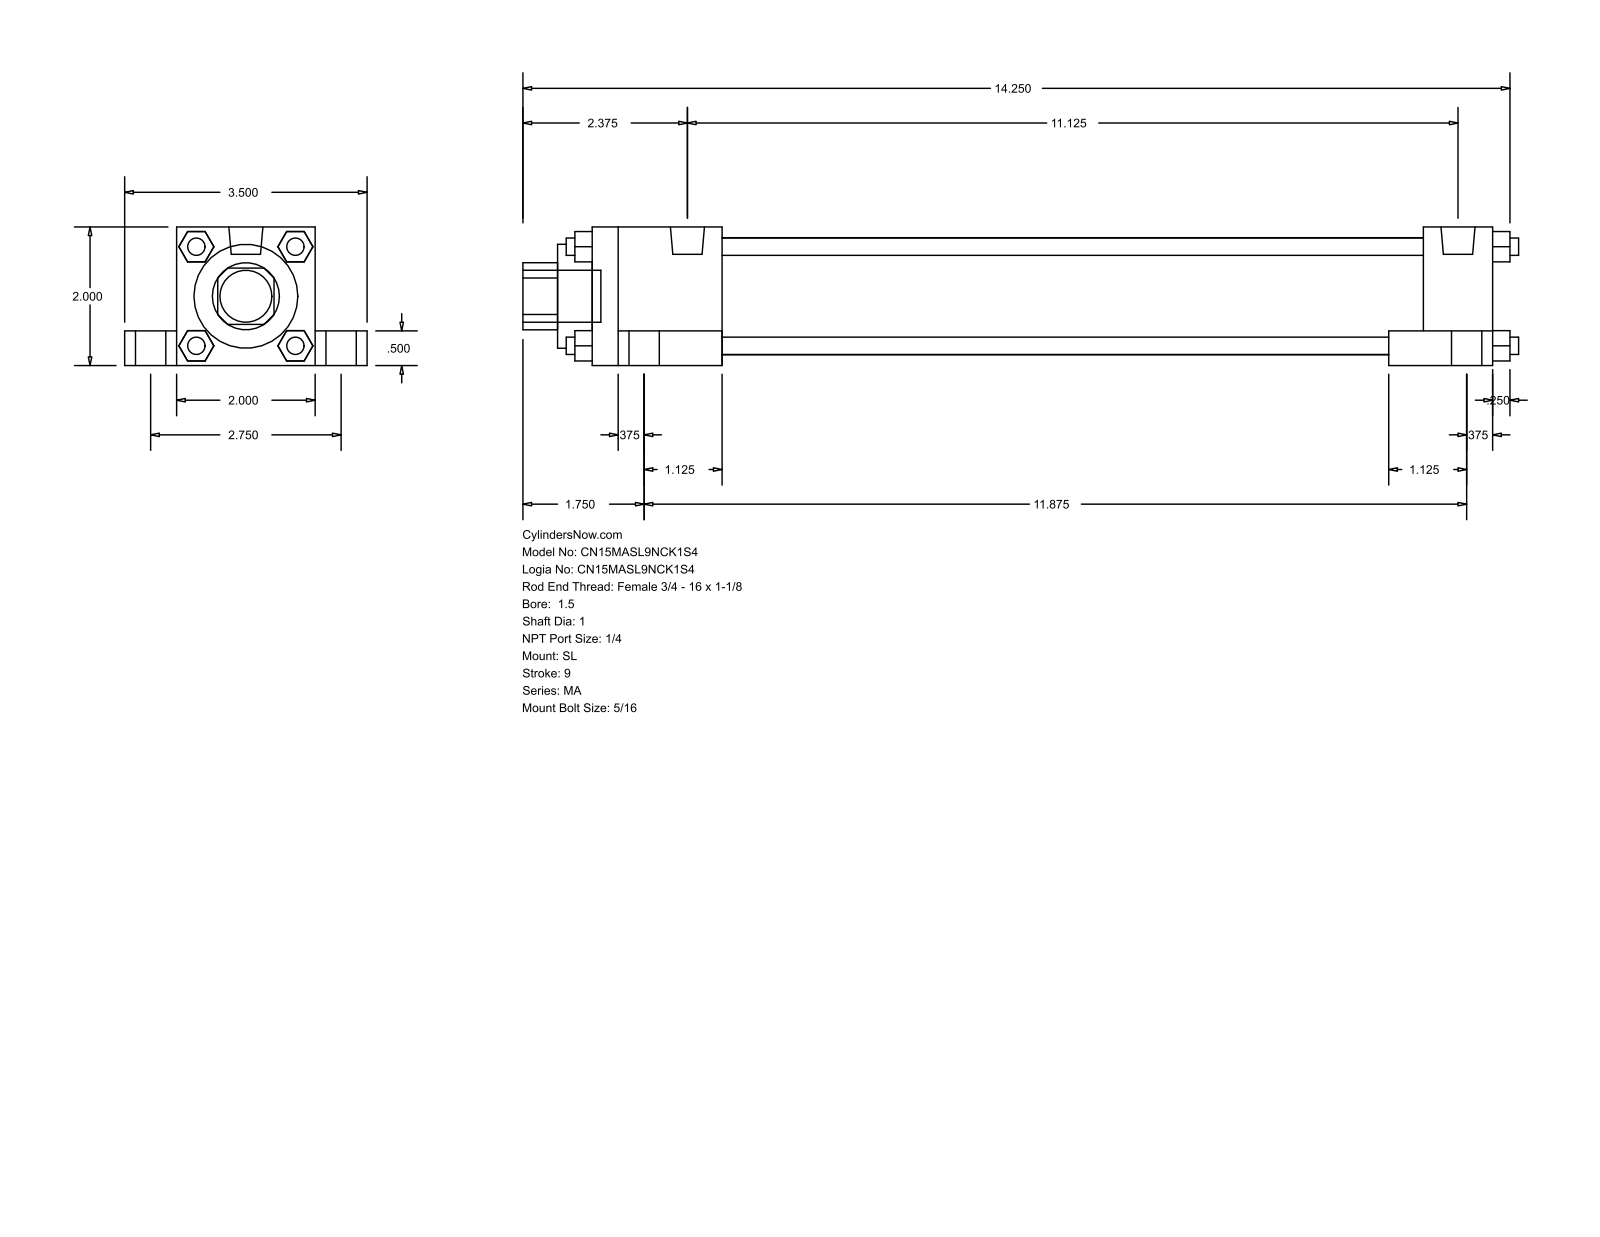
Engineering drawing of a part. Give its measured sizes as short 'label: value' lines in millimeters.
name: MA_SL__0150_1
written by: GSSL Pune (CONFIG_CONTROL_DESIGN)
unit: mm
bodies: 0 solids, 148 faces (112 planar, 36 cylindrical, 0 other)
size: 365.12 × 88.9 × 50.8
holes: 1× ⌀25.4, 1× ⌀38.1, 1× ⌀42.93
bosses: 4× ⌀17.46, 4× ⌀11.11, 4× ⌀7.94, 4× ⌀6.35, 2× ⌀12.49, 1× ⌀19.05
rounds: 1× R12.29
face distances: 50.8, 12.7, 19.05, 9.52, 69.85, 38.1, 6.35, 330.2, 25.4, 304.8
